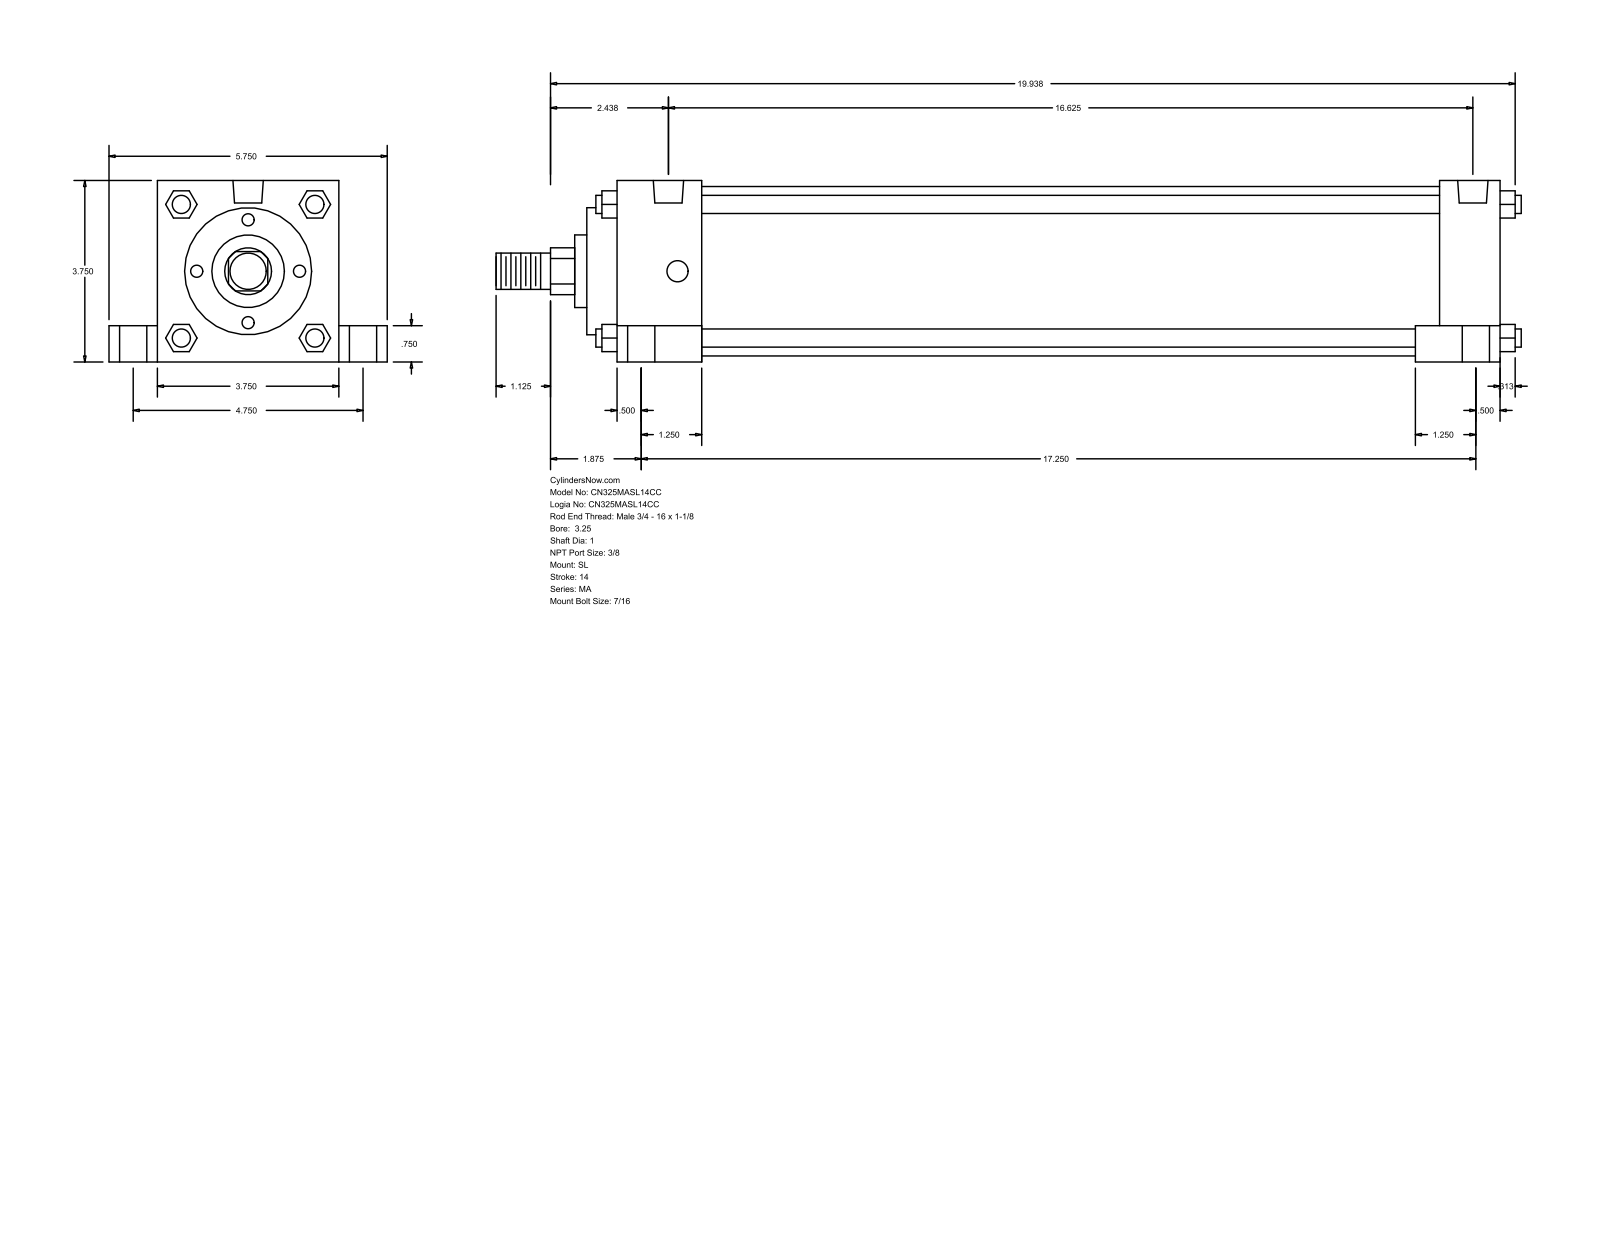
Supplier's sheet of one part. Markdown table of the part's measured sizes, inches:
| quantity | value |
| --- | --- |
| part name | MA_SL__0325_1 |
| STEP written by | GSSL Pune (CONFIG_CONTROL_DESIGN) |
| units | inches |
| bodies | 0 solids, 150 faces (113 planar, 37 cylindrical, 0 other) |
| overall size | 21.187 × 5.75 × 3.75 |
| round holes (diameter × count) | 0.437 × 4, 0.563 × 4, 0.813 × 4, 0.627 × 2 |
| round bosses / shafts (diameter × count) | 0.375 × 4, 3.5 × 1, 2.625 × 1, 1.5 × 1, 1 × 1, 0.75 × 1 |
| partial cylindrical surfaces (radius × count) | 0.484 × 1 |
| main face-to-face distances | 3.75, 18.25, 15.25, 0.625, 1, 4.75, 0.75, 17, 1.25, 1.75 |
| hole center spacings | 0.187, 2.376, 2.388, 2.441, 2.491, 4.75, 16.25, 16.438 |
